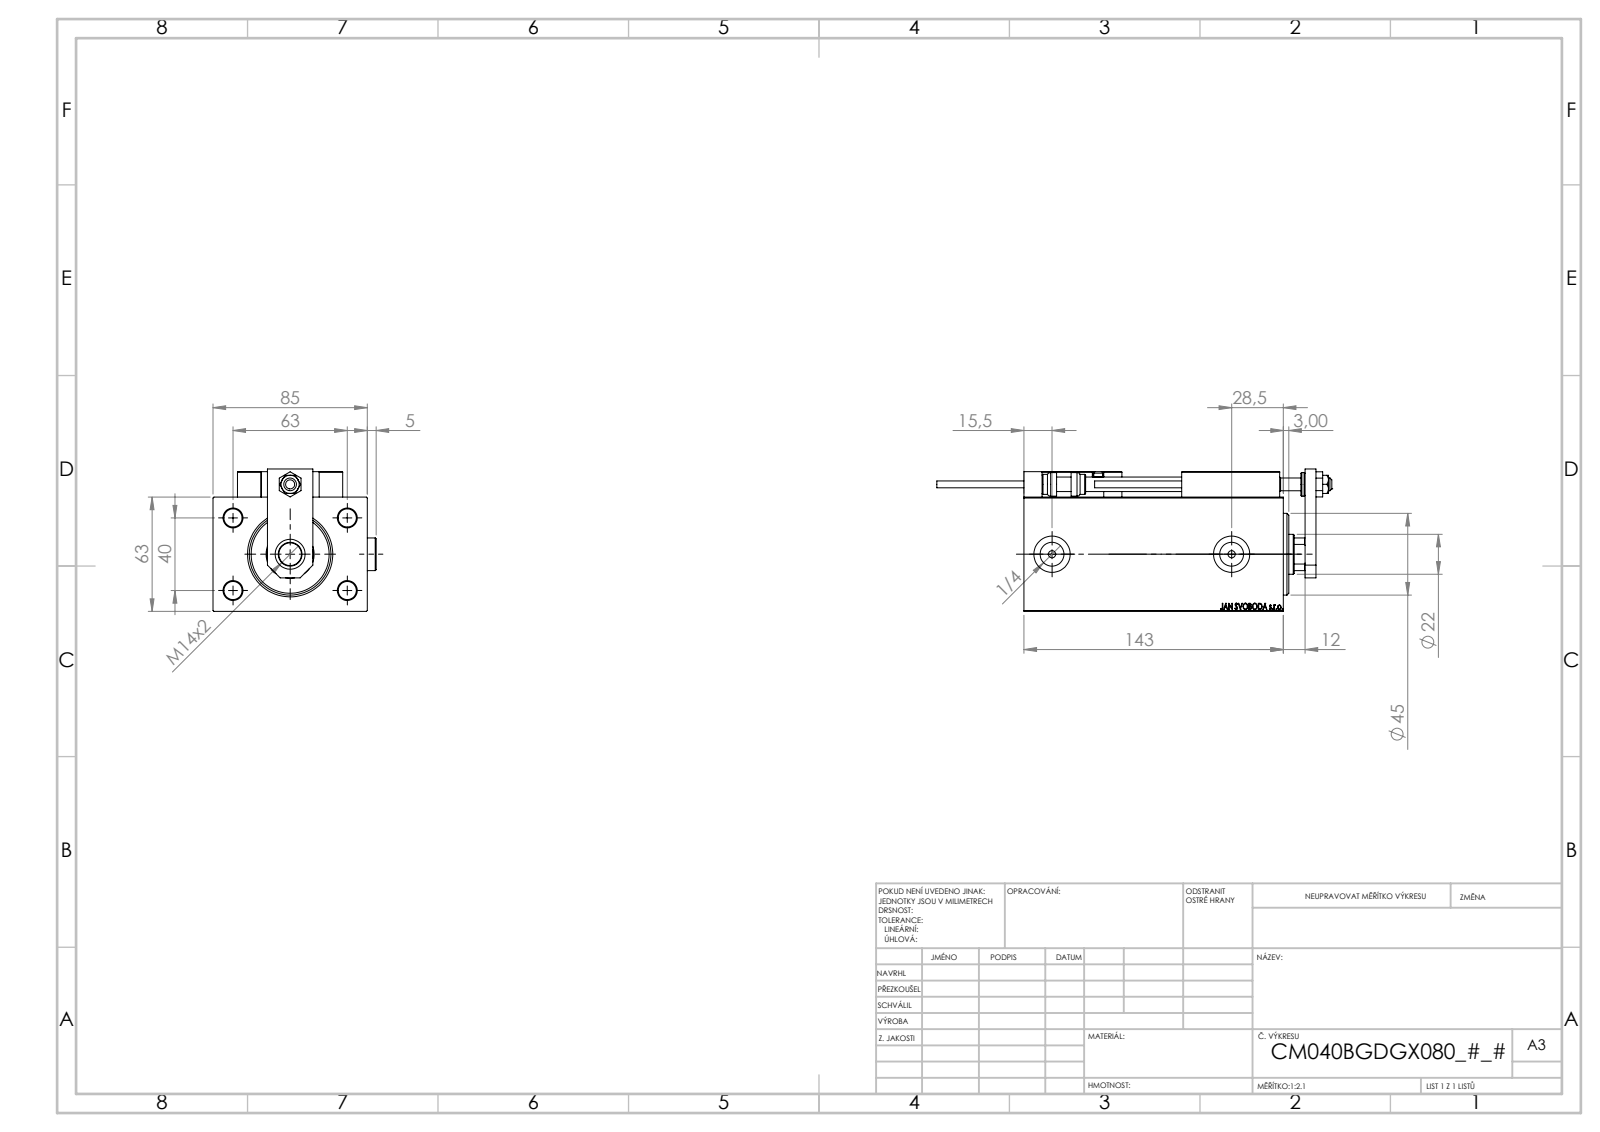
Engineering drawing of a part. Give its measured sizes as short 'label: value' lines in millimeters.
name: ALLEN BOLT D5; MAGNET; ALLEN BOLT D8; ZARAZKA (+8 more)
written by: SolidWorks 2019 (CONFIG_CONTROL_DESIGN)
unit: mm
bodies: 26 solids, 1372 faces (595 planar, 200 cylindrical, 577 other)
size: 217.7 × 89.9 × 78.5
volume: 733 469 mm³; area: 125 862 mm²
holes: 6× ⌀4, 5× ⌀8, 4× ⌀3.2, 4× ⌀10, 2× ⌀5, 2× ⌀13.16, 2× ⌀20, 1× ⌀7, 1× ⌀12.5, 1× ⌀16.5, 1× ⌀22, 1× ⌀25.5
bosses: 2× ⌀18, 2× ⌀5, 2× ⌀3.8, 1× ⌀13, 1× ⌀11
rounds: 30× R0.3, 2× R3, 1× R10.5
face distances: 63, 85, 12, 143, 131, 14, 77, 18, 30, 13.5
hole spacings: 37.31, 11.37, 20, 29.59, 29.69, 36.06, 36.53, 40
